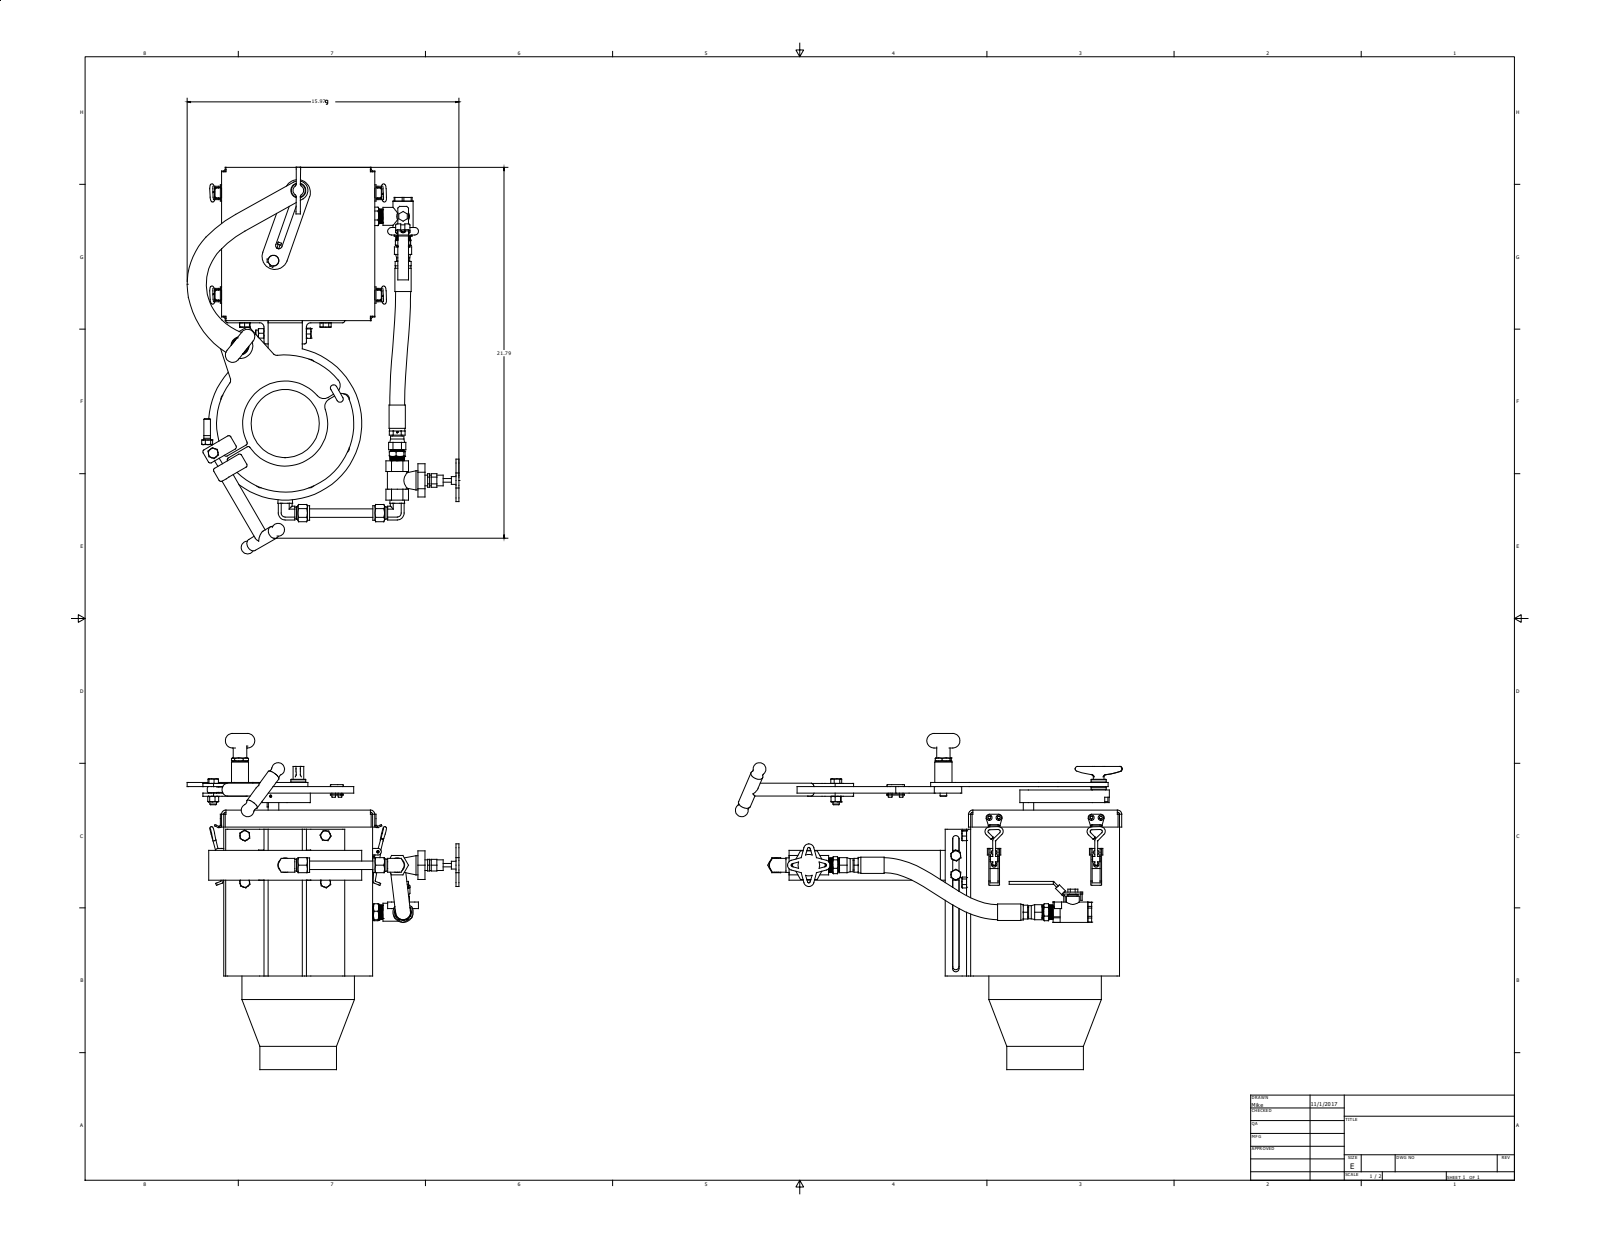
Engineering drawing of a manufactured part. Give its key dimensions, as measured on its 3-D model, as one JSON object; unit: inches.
{"part_name": "WPO-2000", "step_written_by": "SolidWorks 2019 (AUTOMOTIVE_DESIGN)", "units": "inches", "bodies": {"solids": 2, "faces": 1687, "planar": 661, "cylindrical": 621, "other": 405}, "overall_size": [21.243, 18.013, 16.299], "volume_in3": 1031, "surface_area_in2": 1157, "round_holes": [[0.625, 6], [0.625, 2], [4, 1], [5.25, 1]], "round_bosses_or_shafts": [[0.173, 16], [0.562, 9], [0.75, 6], [1.2, 4], [1.1, 4], [0.375, 3], [0.315, 3], [0.219, 2]], "partial_cylinders_radius": [[0.006, 52], [0.079, 18], [0.125, 12], [0.174, 12], [0.063, 10], [0.142, 10], [0.197, 6], [0.3, 6]], "face_to_face_distances": [8.749, 1.476, 9, 6.462, 4.712, 1.75, 6.187, 7.937, 0.25, 3], "hole_center_spacings": [2.87, 3.75, 5.303, 6.929, 7.5]}
